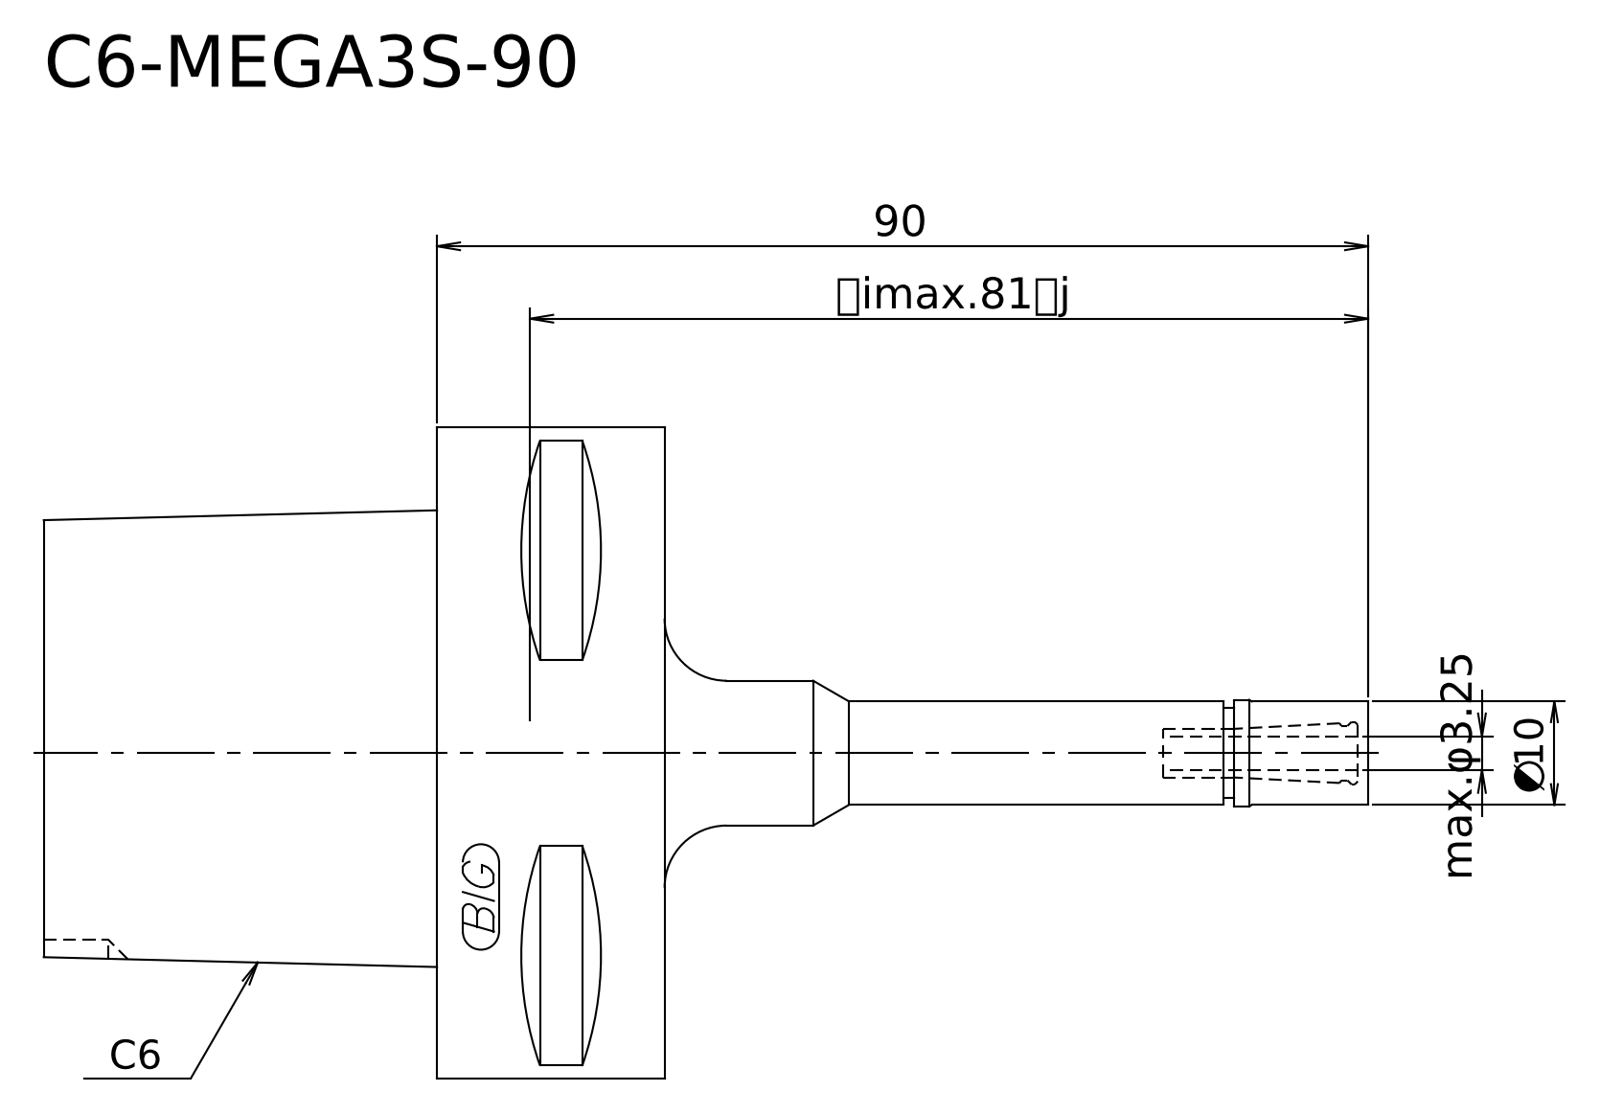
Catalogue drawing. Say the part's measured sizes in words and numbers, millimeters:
The part is named "MGN3S_1.stp; C6-MEGA3S-90-030_ASM.stp; C6-MEGA3S-90-030-FreeParts; DXF_TEMP_ASSY_ASM_4_ASM.stp (+3 more)". Its 3-D file was written by "SolidWorks 2019 (CONFIG_CONTROL_DESIGN)". It is 2 solids with 97 faces: 38 planar, 41 cylindrical and 18 other. Overall it measures 128 by 63 by 63 millimeters. Its volume is 102 989 cubic millimeters and its surface area 23 946 square millimeters. Round holes: 1 of diameter 3.3, 1 of diameter 3.4, 1 of diameter 4.5, 1 of diameter 4.7, 1 of diameter 6.6, 1 of diameter 8.1, 1 of diameter 8.2, 1 of diameter 8.7, 1 of diameter 18, 1 of diameter 28, 1 of diameter 32. Round bosses or shafts: 1 of diameter 63, 1 of diameter 14, 1 of diameter 10.3, 1 of diameter 10. Partial cylindrical surfaces (rounded edges, fillets, slot ends): 1 of radius 5. The main face-to-face distances are 22, 27, 60, 38, 11, 33, 24.89, 54, 55.4, 6.
